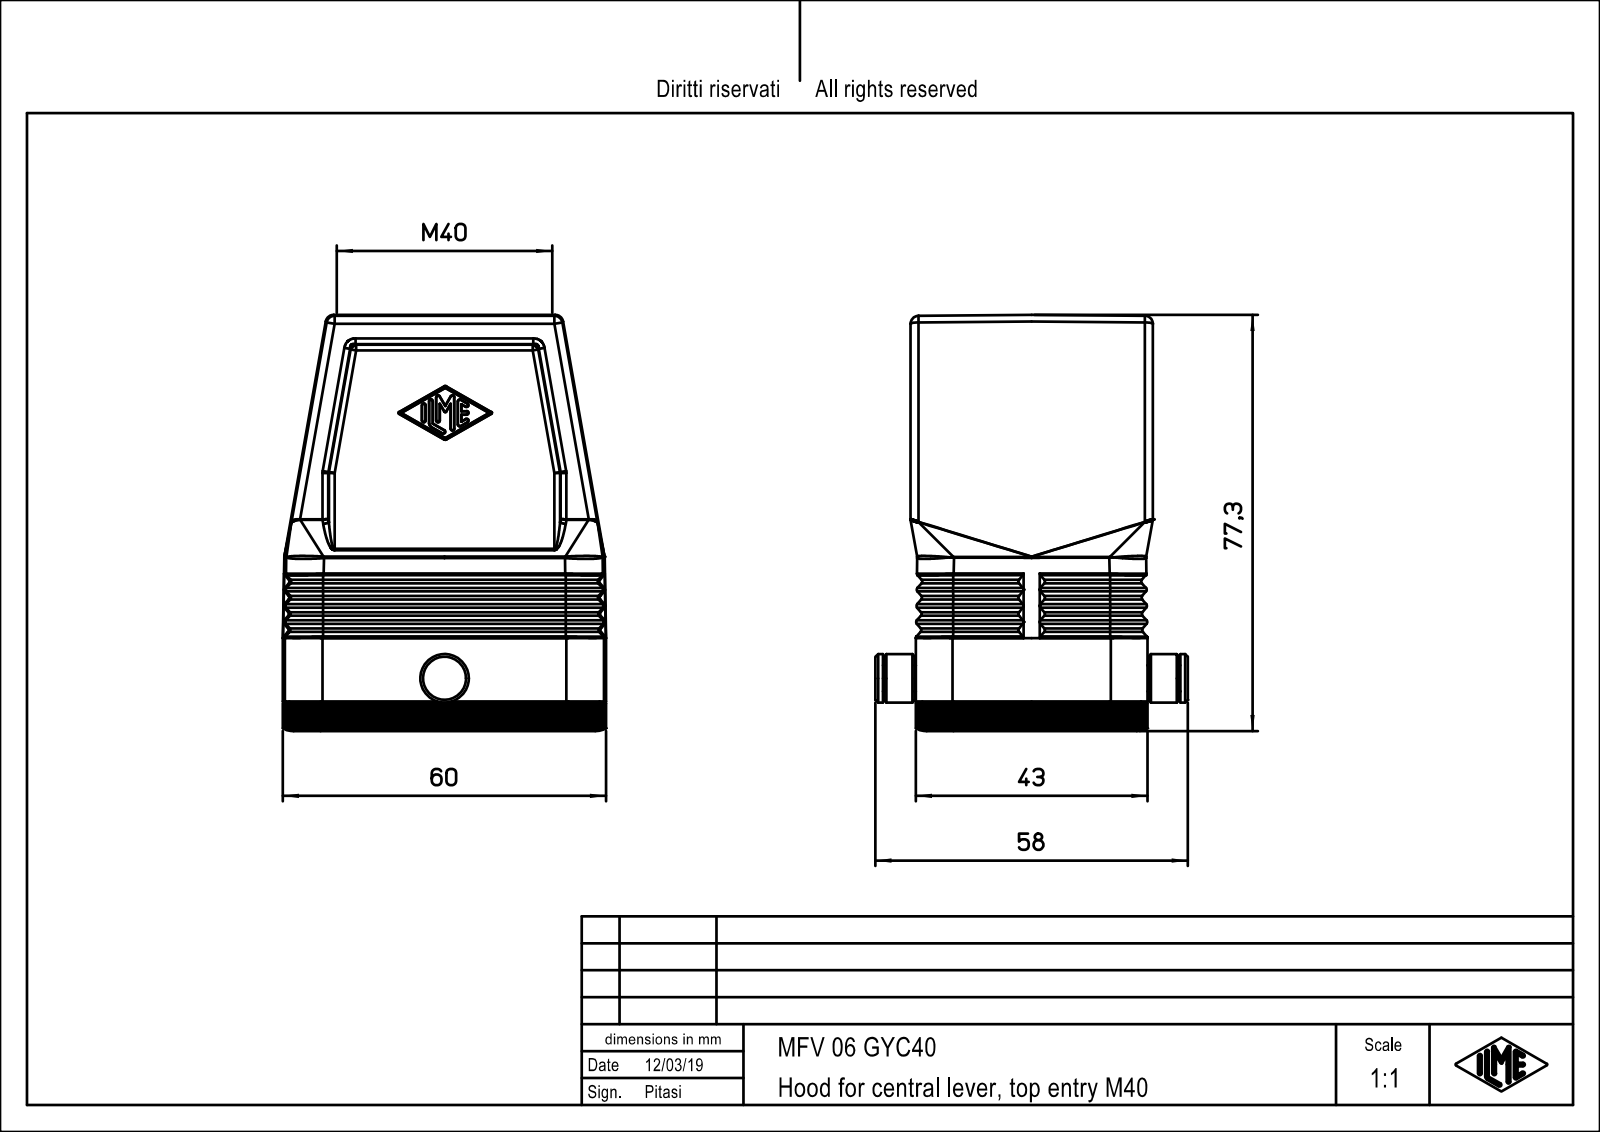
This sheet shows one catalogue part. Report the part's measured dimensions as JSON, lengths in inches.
{"part_name": "MFV_06_GYC40", "step_written_by": "PTC Creo Elements/Direct Modeling 19.0E 27-Jun-2016 (C) Parametric Technology GmbH (AUTOMOTIVE_DESIGN)", "units": "inches", "bodies": {"solids": 1, "faces": 518, "planar": 172, "cylindrical": 168, "other": 178}, "overall_size": [3.041, 2.362, 2.283], "volume_in3": 3.633, "surface_area_in2": 48.29, "round_holes": [[0.118, 4], [1.575, 1]], "round_bosses_or_shafts": [[0.354, 1], [0.189, 1]], "partial_cylinders_radius": [[0.02, 54], [0.059, 44], [0.118, 12], [0.276, 12], [0.157, 4], [0.165, 4], [0.228, 4]], "face_to_face_distances": [1.693, 0.276, 0.157, 0.079, 0.297, 0.039, 1.732, 2.362, 1.535, 0.197], "hole_center_spacings": [1.016, 1.063, 1.732, 2.032]}
